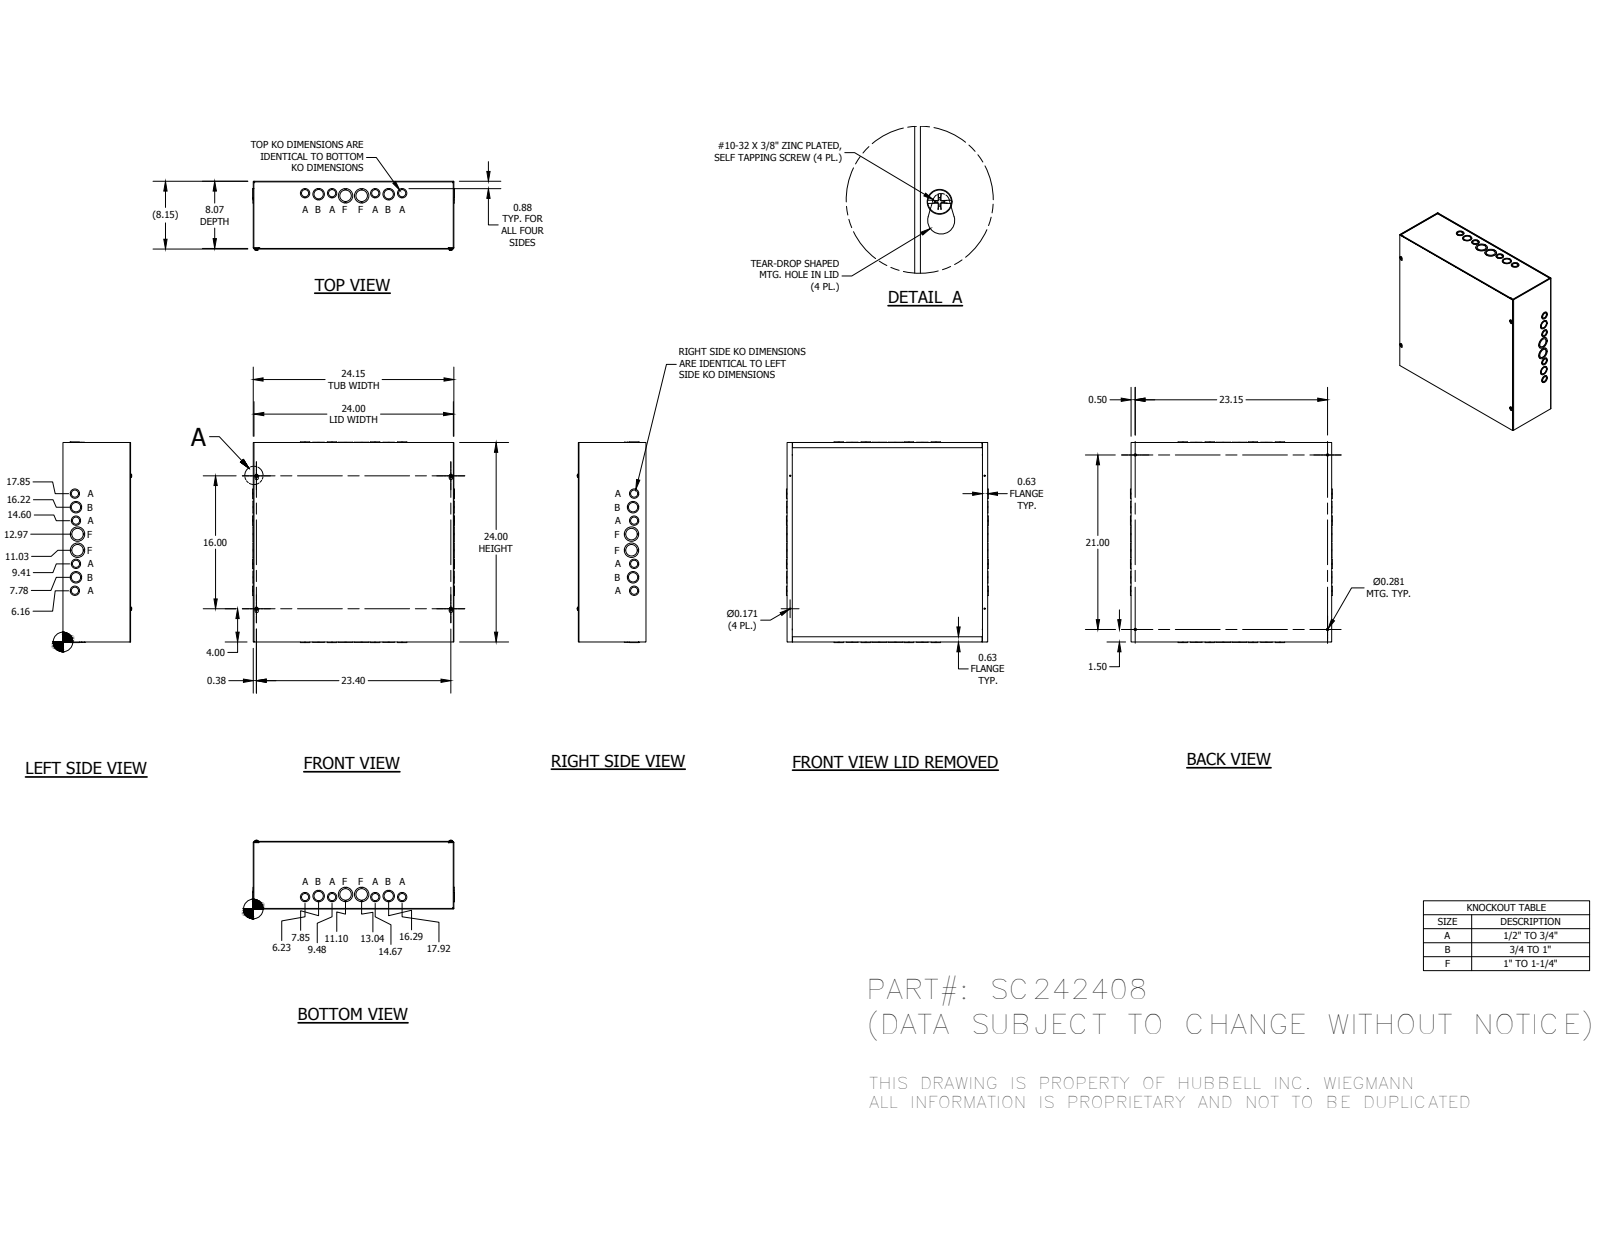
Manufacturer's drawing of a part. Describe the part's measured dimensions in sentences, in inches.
The part is named "SC242408BLR; SC2408TB; SC2424LPA; 37214 (+1 more)". Its 3-D file was written by "Autodesk Inventor 2014 (AUTOMOTIVE_DESIGN)". It is 37 solids with 1219 faces: 899 planar, 236 cylindrical and 84 other. Overall it measures 24.296 by 24.148 by 8.28 inches. Round holes: 14 of diameter 1.125, 10 of diameter 0.875, 8 of diameter 1.375, 4 of diameter 0.171, 4 of diameter 0.281, 4 of diameter 1.75. Round bosses or shafts: 4 of diameter 0.19. Partial cylindrical surfaces (rounded edges, fillets, slot ends): 12 of radius 0.016, 12 of radius 0.09, 4 of radius 0.125, 4 of radius 0.203. The main face-to-face distances are 0.074, 8.074, 8, 8.148, 24, 24.074, 23.926, 24.148, 23.852, 0.148. The hole center spacings are 1.63, 1.63, 1.655, 2.503, 3.25, 3.256, 3.579, 4.885.
